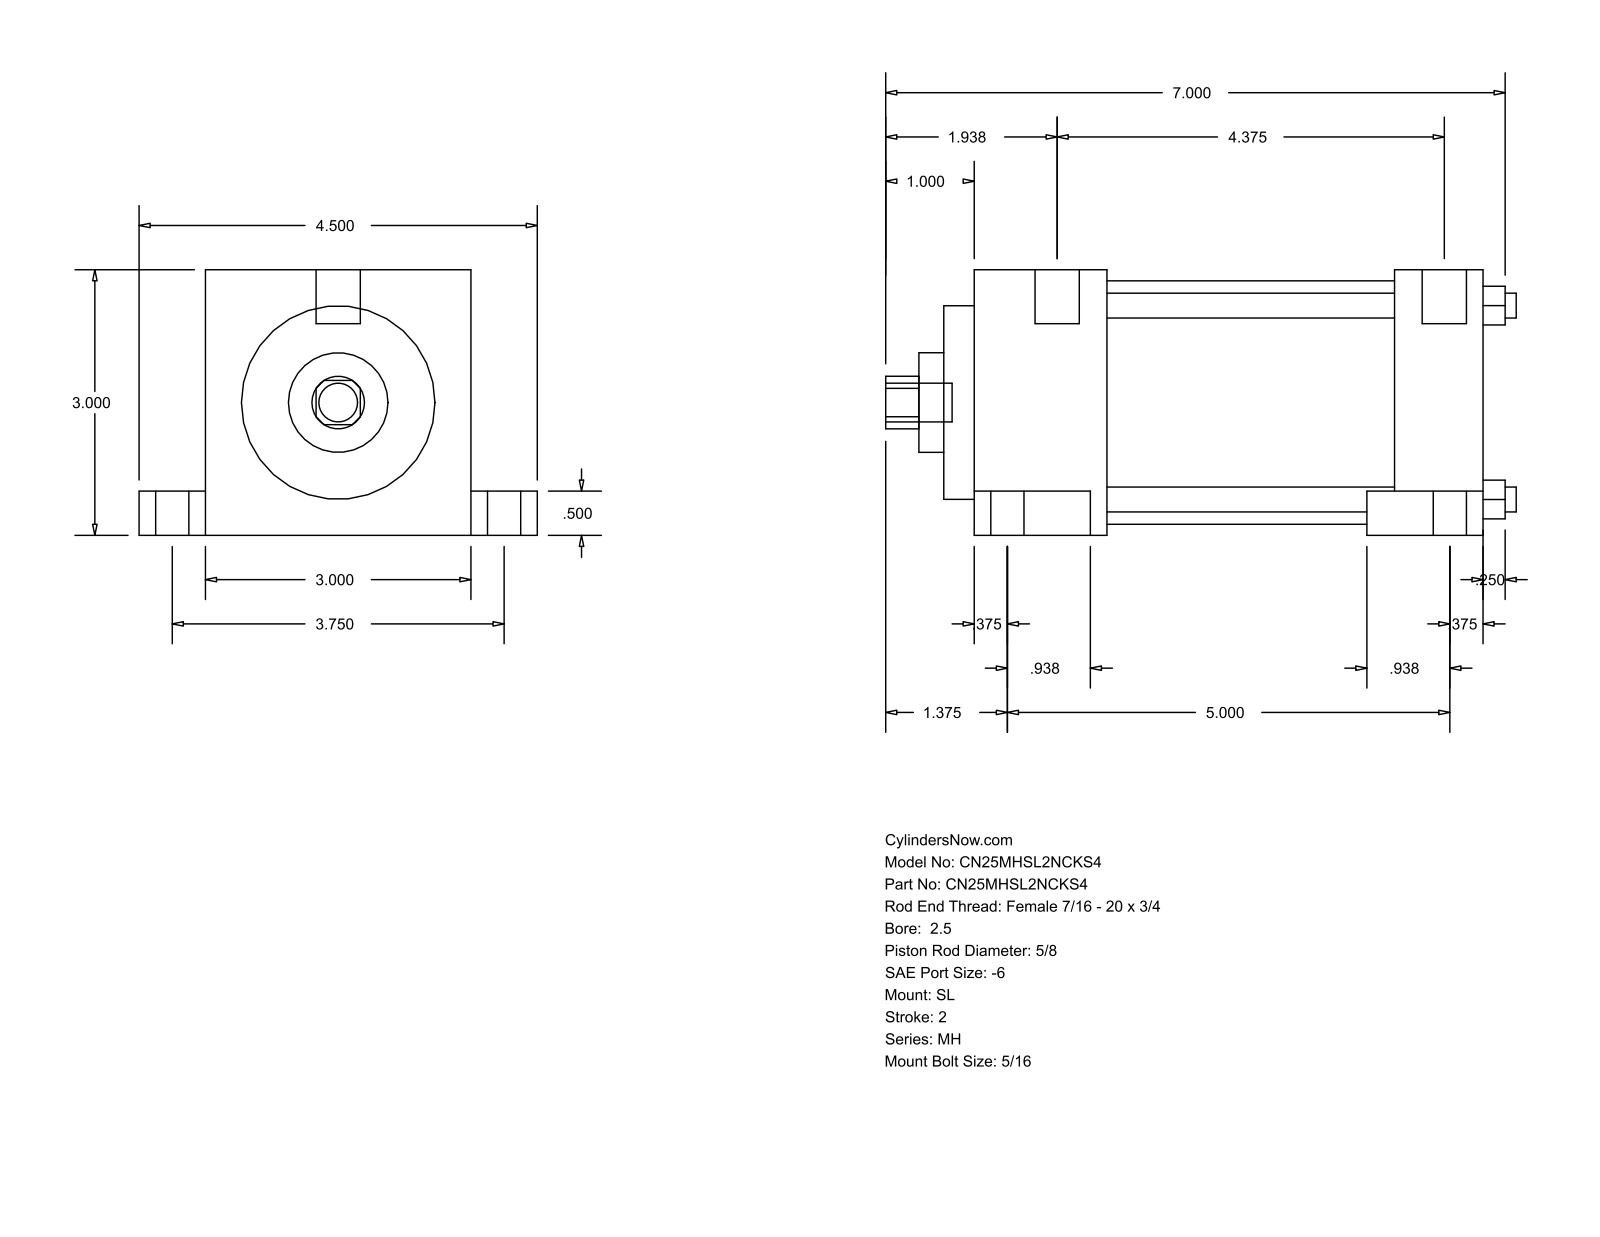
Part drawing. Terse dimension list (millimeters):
name: MH_SL__0250_0.625
written by: GSSL Pune (CONFIG_CONTROL_DESIGN)
unit: mm
bodies: 0 solids, 86 faces (61 planar, 25 cylindrical, 0 other)
size: 180.97 × 114.3 × 76.2
holes: 4× ⌀7.14, 1× ⌀15.88, 1× ⌀28.57, 1× ⌀55.55, 1× ⌀69.85
bosses: 2× ⌀15.88, 2× ⌀9.53, 2× ⌀5.56, 1× ⌀12.7, 1× ⌀11.11
rounds: 1× R7.54
face distances: 76.2, 25.4, 129.38, 154.78, 12.7, 63.5, 19.05, 95.25, 161.92, 31.75
hole spacings: 39.33, 55.62, 78.66
